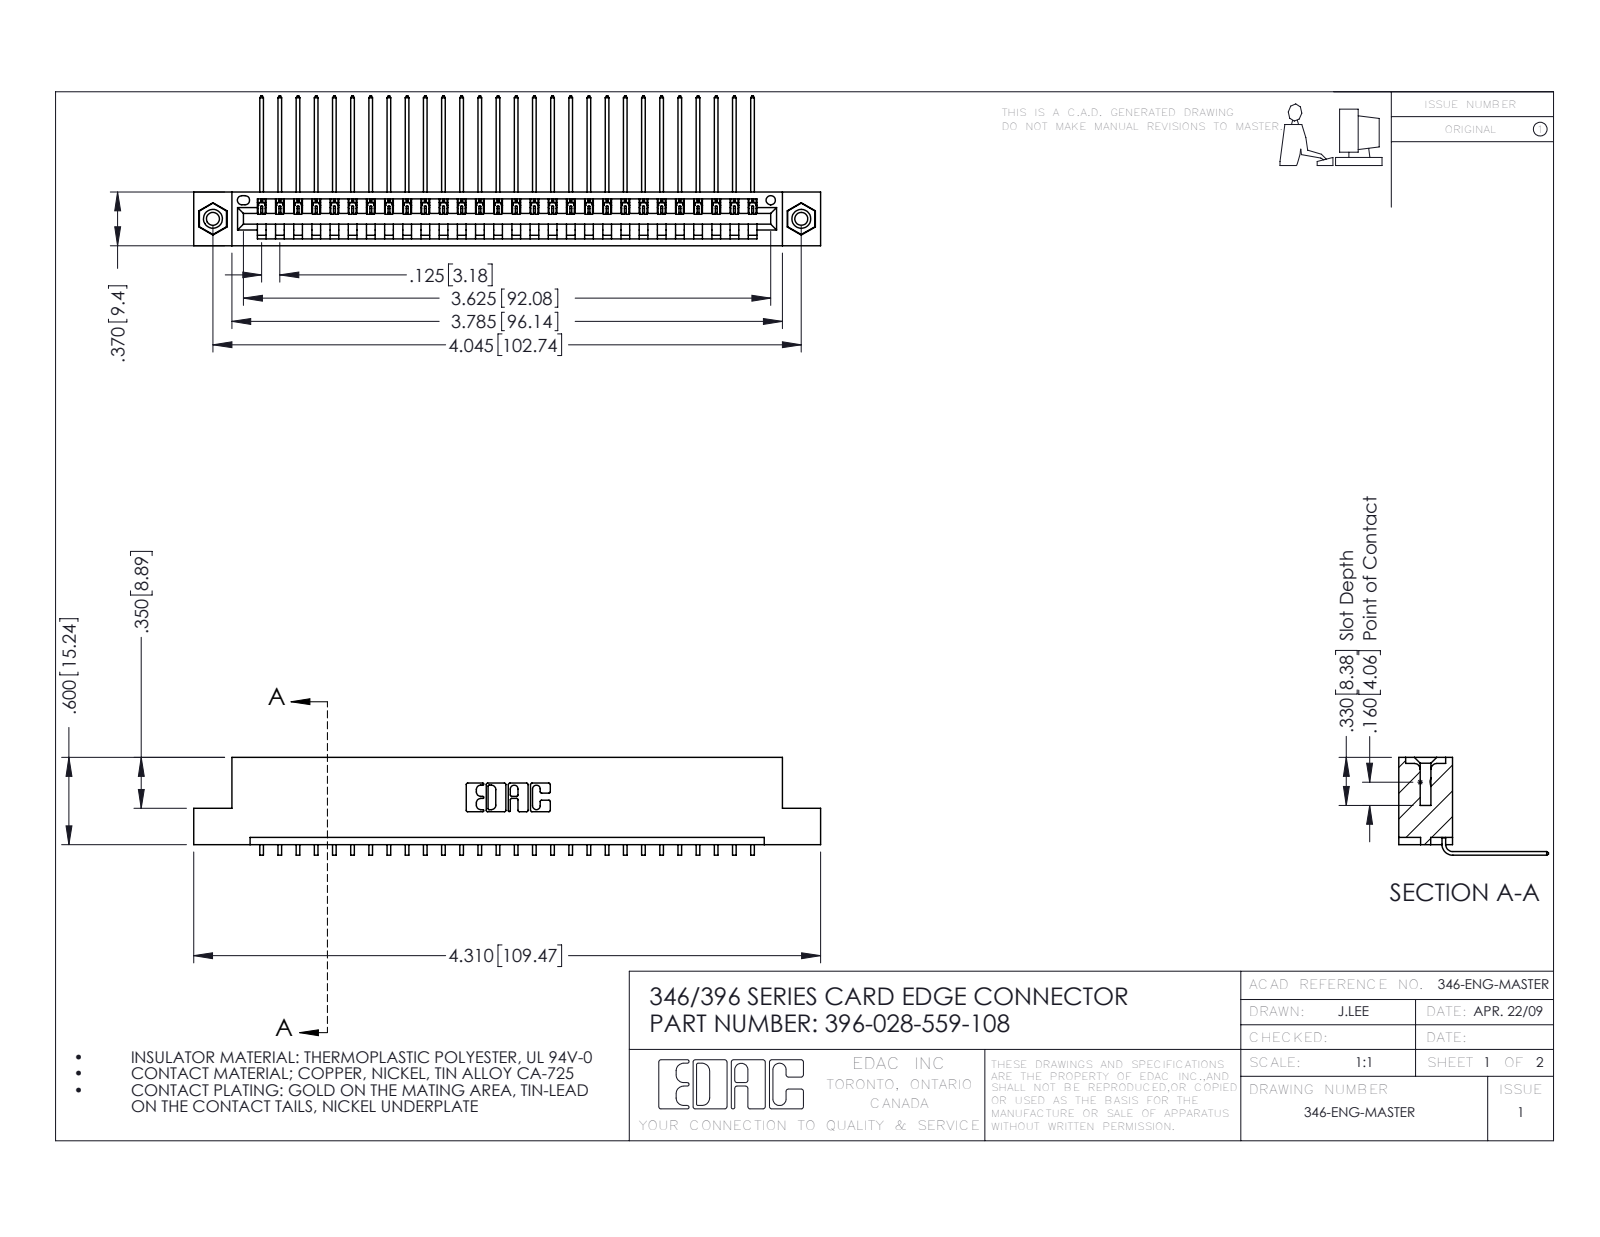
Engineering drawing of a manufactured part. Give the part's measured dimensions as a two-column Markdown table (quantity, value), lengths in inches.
| quantity | value |
| --- | --- |
| part name | 396-028-559-108; 346 Part_Flush Mounting Lugs - 0.156 Dia-TI; 345-250-001_345-250-003-102; 345-292-001_558 559 Tail - 1 |
| STEP written by | SolidWorks 2016 (CONFIG_CONTROL_DESIGN) |
| units | inches |
| bodies | 31 solids, 1862 faces (1284 planar, 562 cylindrical, 16 other) |
| overall size | 4.31 × 1.03 × 0.673 |
| volume | 0.639 in³ |
| surface area | 20.94 in² |
| round holes (diameter × count) | 0.089 × 2, 0.125 × 2, 0.156 × 2, 0.064 × 1 |
| round bosses / shafts (diameter × count) | 0.155 × 2 |
| partial cylindrical surfaces (radius × count) | 0.006 × 56, 0.01 × 22, 0.007 × 6, 0.031 × 6, 0.026 × 3, 0.031 × 2, 0.04 × 2, 0.014 × 1 |
| main face-to-face distances | 0.048, 0.322, 0.37, 0.25, 0.072, 0.025, 0.298, 0.148, 0.222, 0.1 |
| hole center spacings | 0.246, 3.837, 4.045 |
